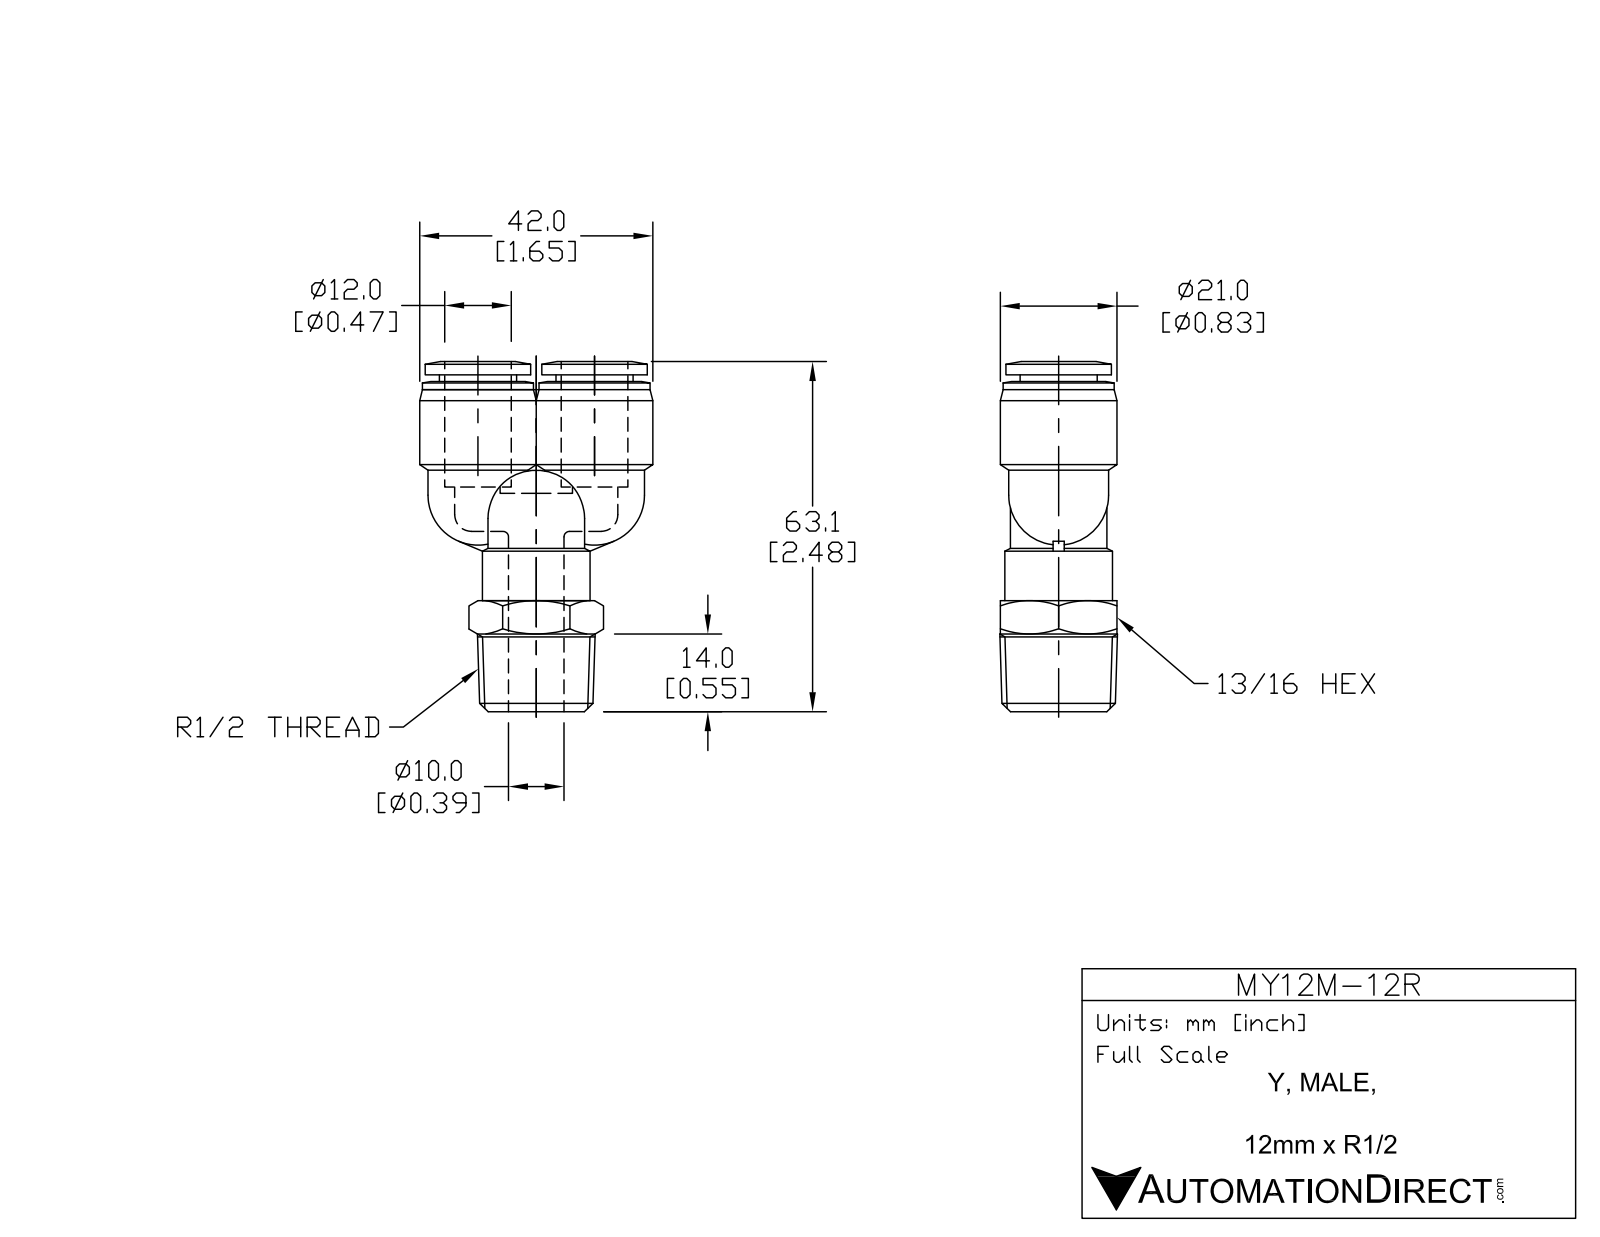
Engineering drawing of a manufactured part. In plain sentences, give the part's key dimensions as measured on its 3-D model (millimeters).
The part is named "MY12M-12R". Its 3-D file was written by "SolidWorks 2015 (AUTOMOTIVE_DESIGN)". It is 1 solid with 106 faces: 23 planar, 34 cylindrical and 49 other. Overall it measures 63.1 by 42 by 21 millimeters. Its volume is 19 160 cubic millimeters and its surface area 10 700 square millimeters. Round holes: 4 of diameter 10, 2 of diameter 12.3. Round bosses or shafts: 2 of diameter 21, 2 of diameter 20, 2 of diameter 19, 2 of diameter 18, 2 of diameter 13.9, 1 of diameter 19.4, 1 of diameter 17.4. The main face-to-face distances are 21, 60.8, 59.5, 1.2, 40.5, 19.1, 20.3, 20, 20.4, 39.5. The hole center spacings are 10.5, 21.
